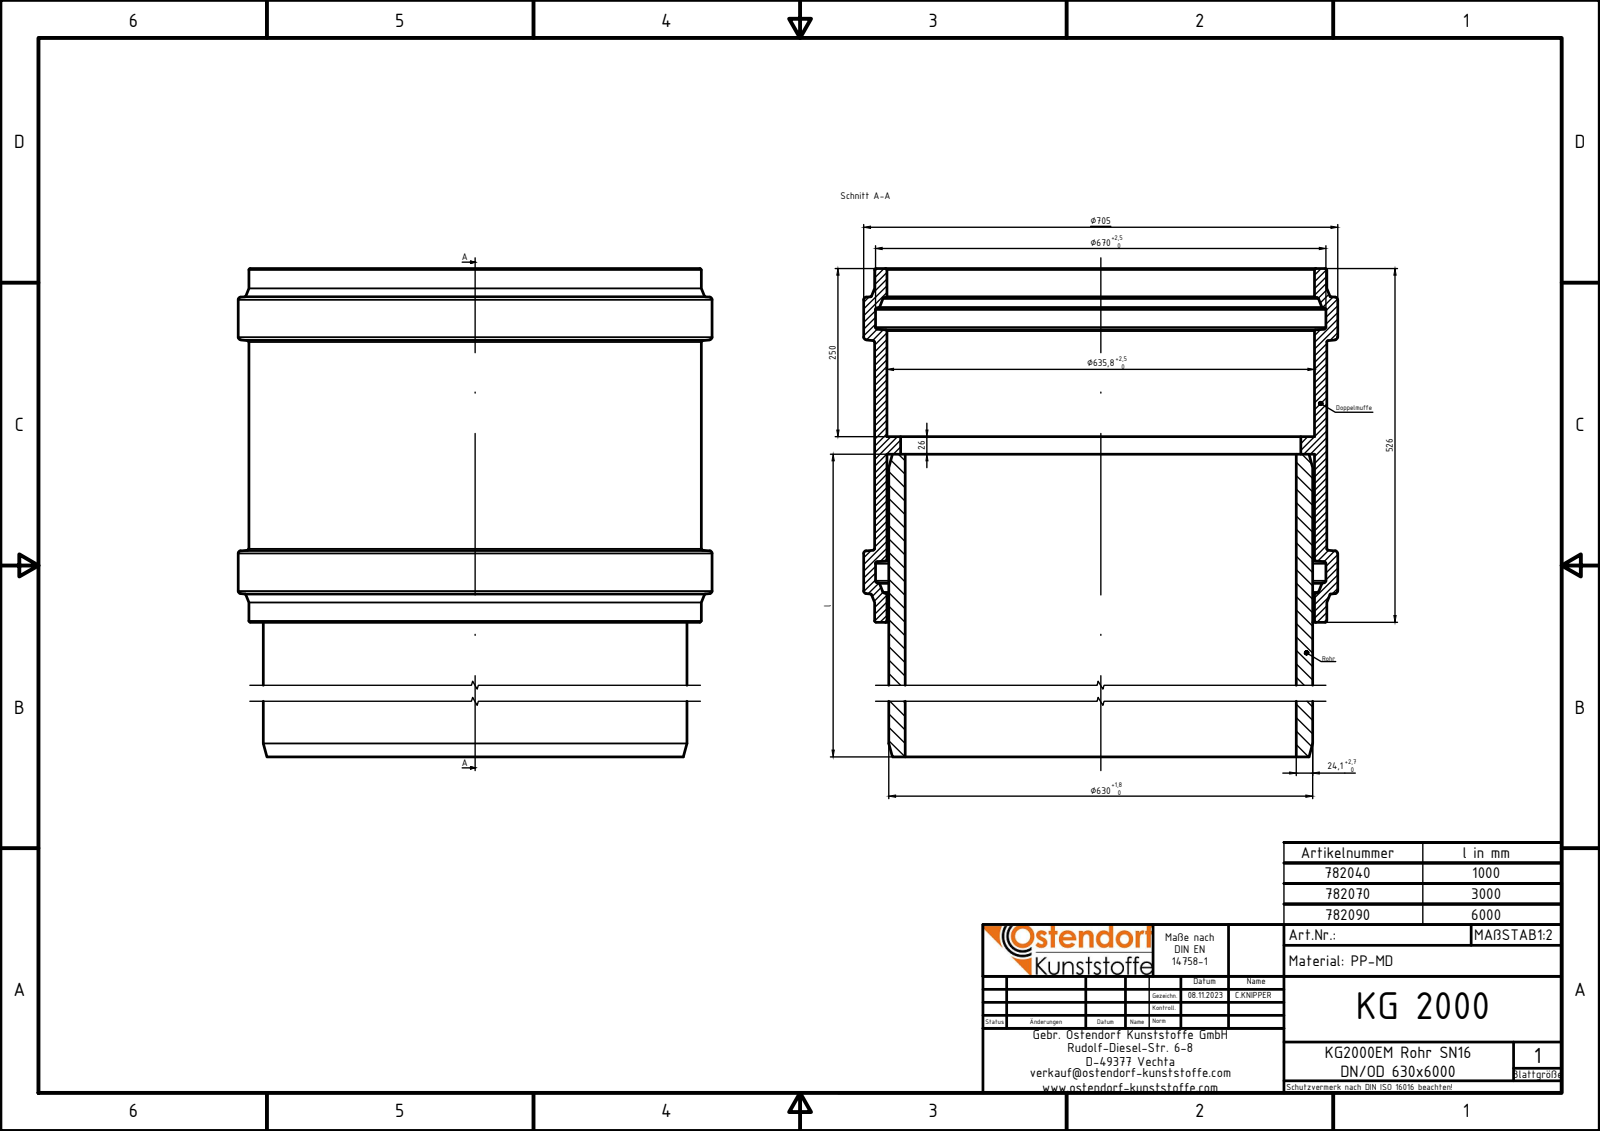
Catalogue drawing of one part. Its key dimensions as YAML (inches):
part_name: "782090z"
step_written_by: "Autodesk Inventor 2024 (AUTOMOTIVE_DESIGN)"
units: inches
bodies: {solids: 1, faces: 60, planar: 6, cylindrical: 14, other: 40}
overall_size: [247.087, 27.748, 27.748]
volume: 18170
surface_area: 39350
round_holes:
  - {diameter: 22.906, count: 1}
  - {diameter: 23.417, count: 1}
  - {diameter: 25.031, count: 1}
  - {diameter: 26.378, count: 1}
round_bosses_or_shafts:
  - {diameter: 27.748, count: 1}
  - {diameter: 26.48, count: 1}
  - {diameter: 24.803, count: 1}
face_to_face_distances: [10.866, 9.843, 237.244, 226.378, 247.087, 20.709, 236.22, 1.024]
